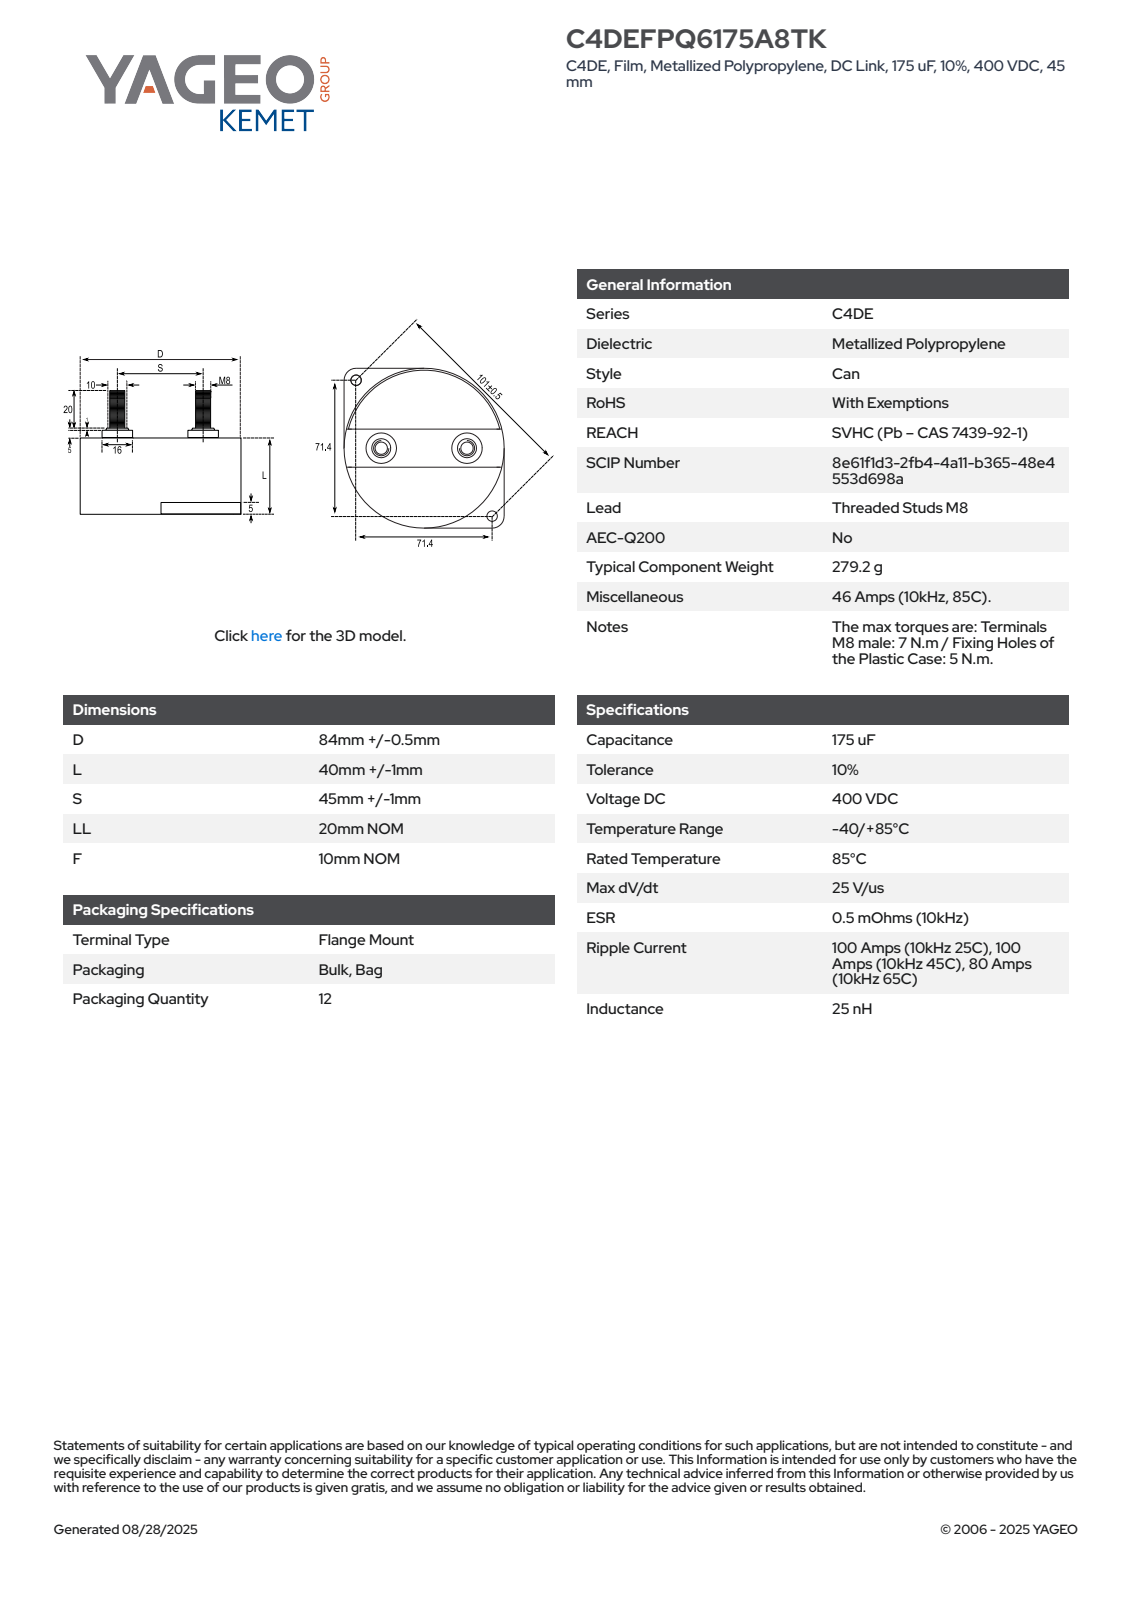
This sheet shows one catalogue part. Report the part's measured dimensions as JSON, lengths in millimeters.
{"part_name": "CFP_C44DE_84X40_D84.5L42S46LL20", "step_written_by": "SolidWorks 2014 (AUTOMOTIVE_DESIGN)", "units": "millimeters", "bodies": {"solids": 1, "faces": 103, "planar": 37, "cylindrical": 31, "other": 35}, "overall_size": [84.51, 84.5, 68], "volume_mm3": 243107, "surface_area_mm2": 25582, "round_holes": [[5.5, 2]], "round_bosses_or_shafts": [[16, 2], [10, 2], [8, 2], [84.5, 1], [80, 1]], "partial_cylinders_radius": [[10, 2], [42.26, 1]], "face_to_face_distances": [42.01, 5, 42, 37.01, 37, 84.5, 47, 4.99, 68, 63], "hole_center_spacings": [101.51]}
